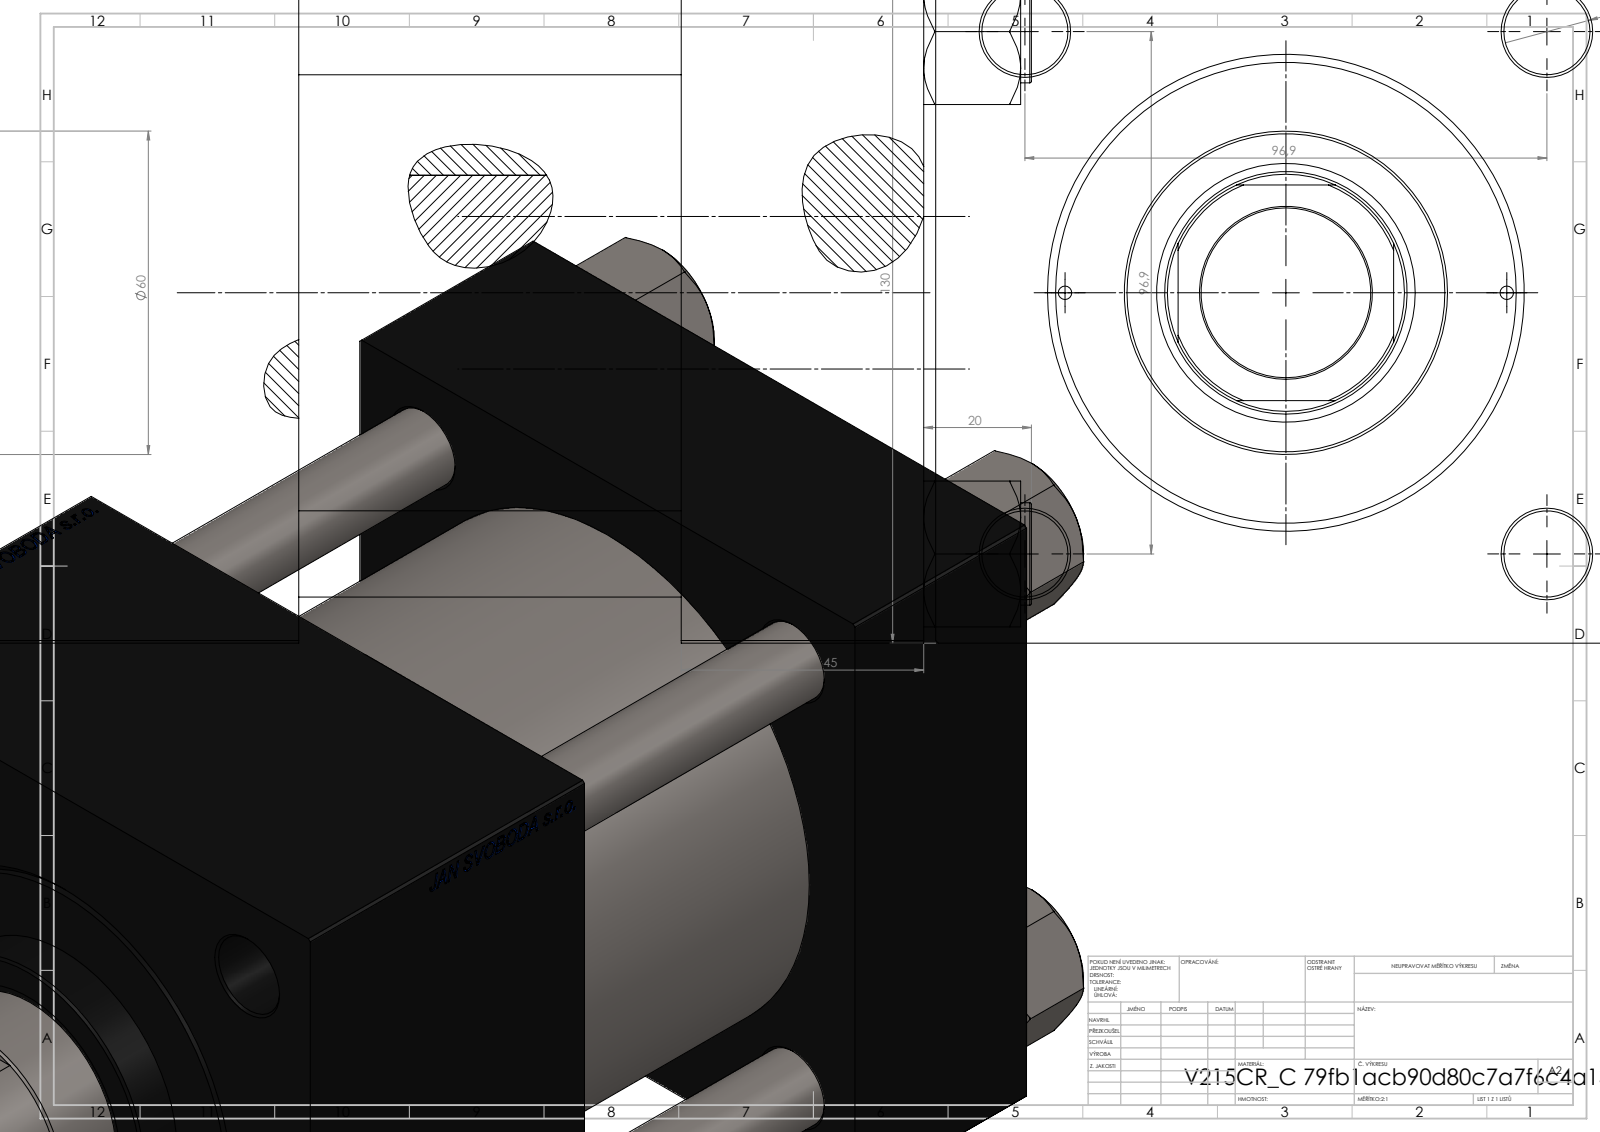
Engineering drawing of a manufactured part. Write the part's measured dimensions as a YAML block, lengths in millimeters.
part_name: "V215CR_C_Body; V215_VC_A; NUT_M5_C; V215CR_C_TYCINKA (+1 more)"
step_written_by: "SolidWorks 2019 (CONFIG_CONTROL_DESIGN)"
units: millimeters
bodies: {solids: 11, faces: 1202, planar: 576, cylindrical: 90, other: 536}
overall_size: [243, 130, 130]
volume: 2425000
surface_area: 326466
round_holes:
  - {diameter: 16, count: 4}
  - {diameter: 2.5, count: 2}
  - {diameter: 7, count: 2}
  - {diameter: 26.44, count: 2}
  - {diameter: 35, count: 2}
  - {diameter: 31.5, count: 1}
  - {diameter: 45, count: 1}
  - {diameter: 48, count: 1}
  - {diameter: 76, count: 1}
  - {diameter: 85.5, count: 1}
  - {diameter: 100, count: 1}
round_bosses_or_shafts:
  - {diameter: 19, count: 4}
  - {diameter: 106, count: 1}
  - {diameter: 60, count: 1}
partial_cylinders:
  - {radius: 22, count: 1}
face_to_face_distances: [130, 45, 188, 143, 116, 71, 72, 20, 96, 51]
hole_center_spacings: [49.02, 68.52, 96.9, 101.73, 41, 137.04, 82, 118.5]
